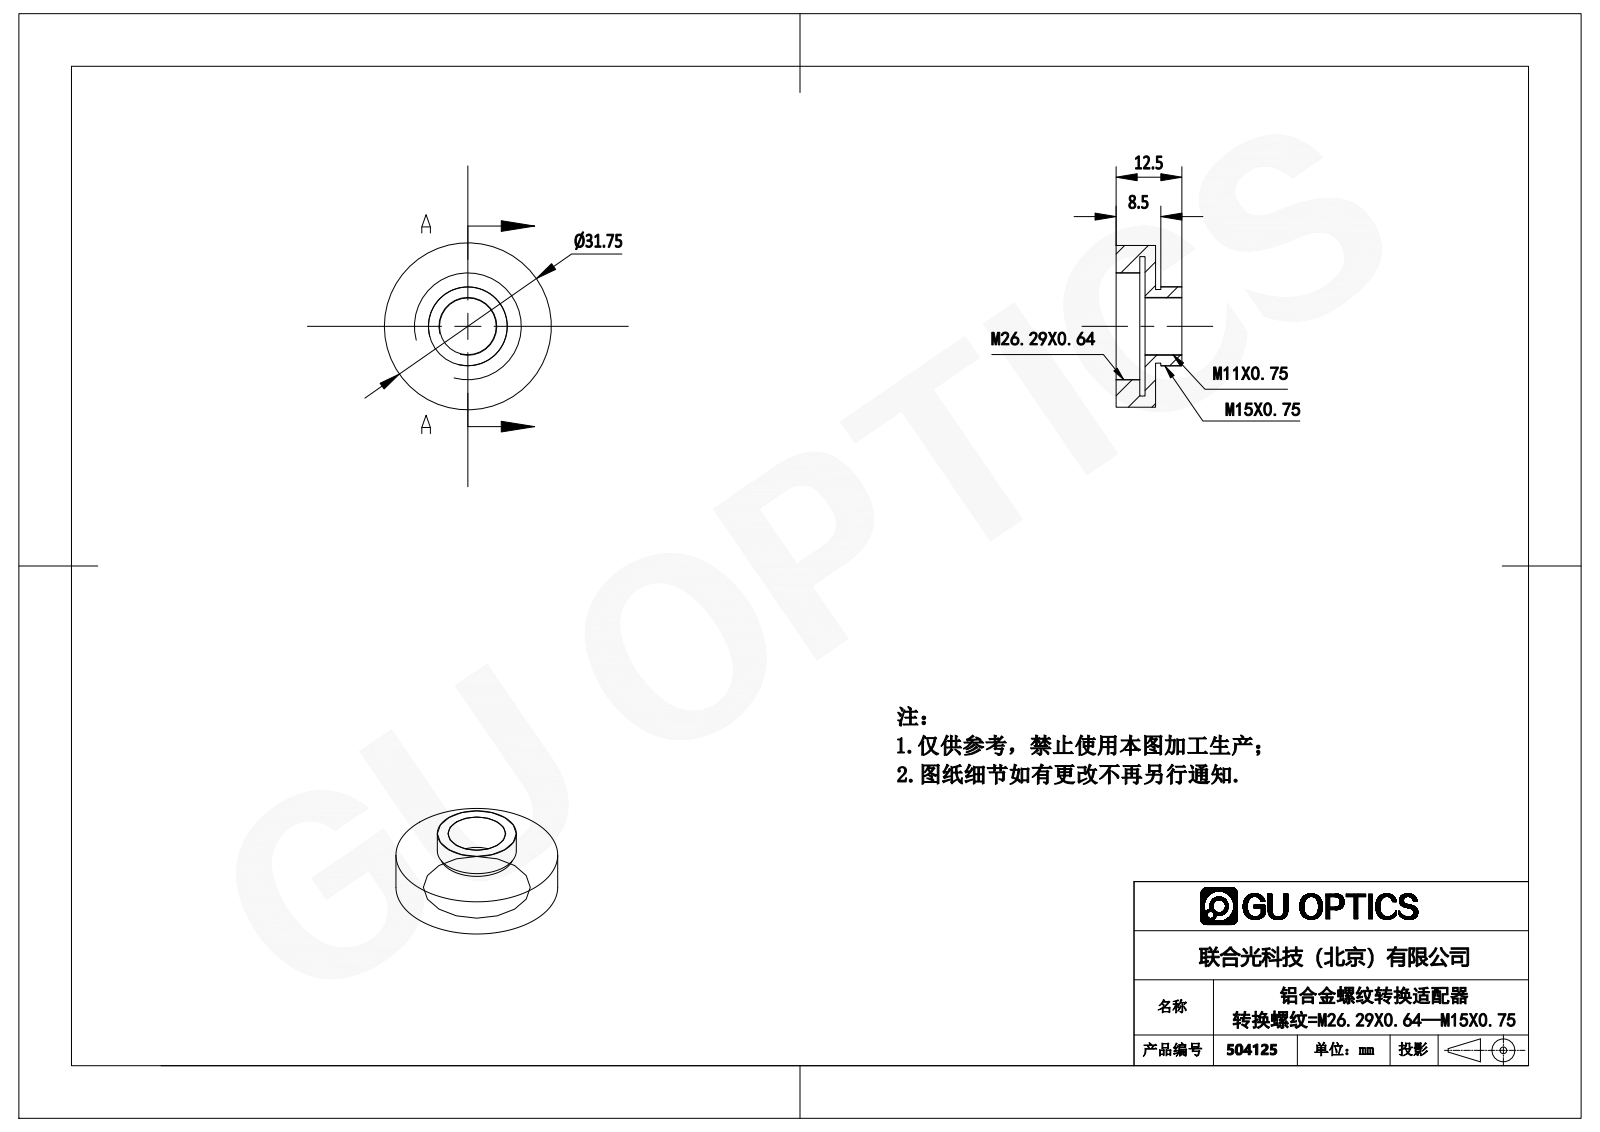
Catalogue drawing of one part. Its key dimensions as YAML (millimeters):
part_name: "504125"
step_written_by: "SolidWorks 2016 (AUTOMOTIVE_DESIGN)"
units: millimeters
bodies: {solids: 1, faces: 18, planar: 6, cylindrical: 12, other: 0}
overall_size: [31.75, 31.75, 12.5]
volume: 4151
surface_area: 3491
round_holes:
  - {diameter: 10.8, count: 1}
  - {diameter: 20.3, count: 1}
  - {diameter: 26.5, count: 1}
round_bosses_or_shafts:
  - {diameter: 31.75, count: 1}
  - {diameter: 15.02, count: 1}
  - {diameter: 14, count: 1}
face_to_face_distances: [7.5, 5.5, 2, 1, 3, 4.5, 12.5, 8, 7, 5]
